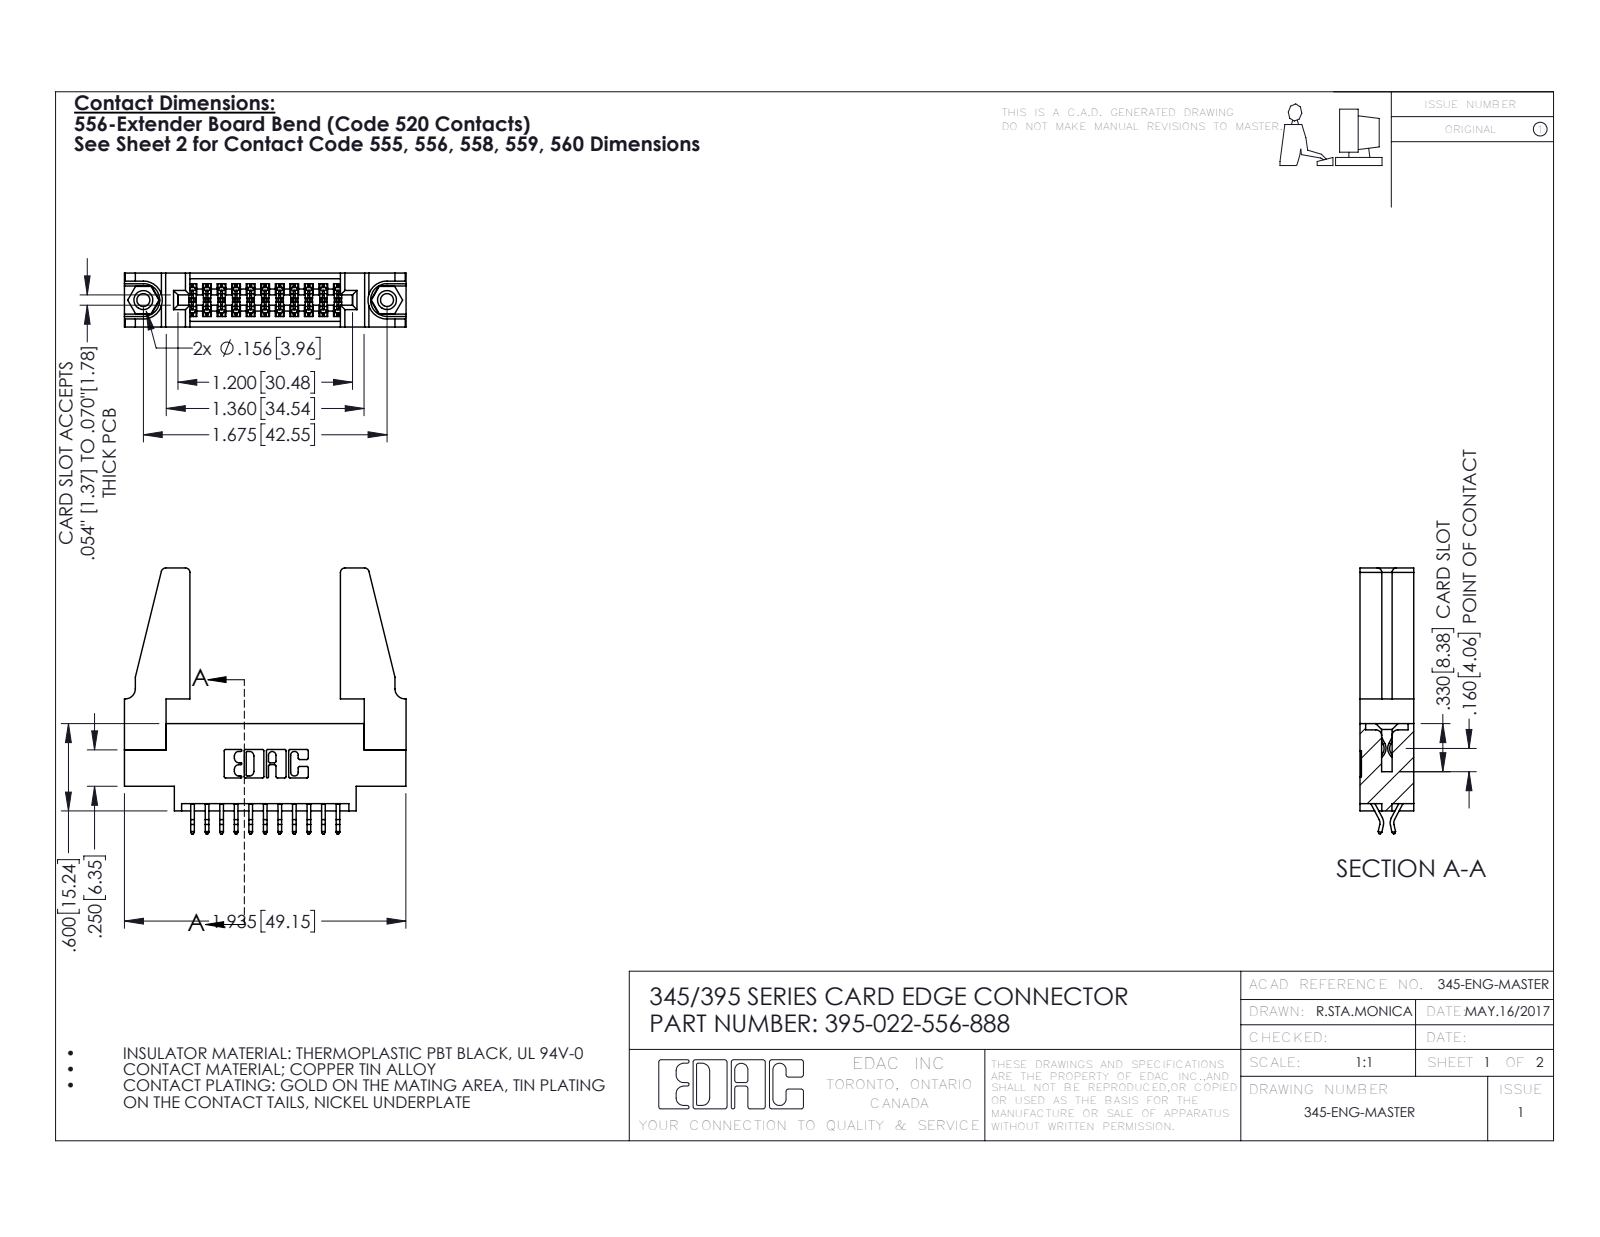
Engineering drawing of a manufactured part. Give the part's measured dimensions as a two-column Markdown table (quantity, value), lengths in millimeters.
| quantity | value |
| --- | --- |
| part name | 345-250-001_345-250-001-102; 345 Part_0.170 Offset - 0.156 Dia-TH; 345-292-001_556 Tail; 395-022-556-888 (+1 more) |
| STEP written by | SolidWorks 2016 (CONFIG_CONTROL_DESIGN) |
| units | millimeters |
| bodies | 27 solids, 1486 faces (970 planar, 500 cylindrical, 16 other) |
| overall size | 49.2 × 46.4 × 9.4 |
| volume | 7 620 mm³ |
| surface area | 9 110 mm² |
| round holes (diameter × count) | 2.3 × 2, 3.2 × 2, 4 × 2, 1.6 × 1 |
| round bosses / shafts (diameter × count) | 3.9 × 2 |
| partial cylindrical surfaces (radius × count) | 0.2 × 33, 0.3 × 22, 0.8 × 8, 0.2 × 6, 0.8 × 6, 0.7 × 3, 0.3 × 2, 0.4 × 2 |
| main face-to-face distances | 9.4, 1.8, 7.6, 5.1, 0.6, 2.5, 6.9, 5.7, 3.8, 3.8 |
| hole center spacings | 6.9, 36.7, 42.5 |
